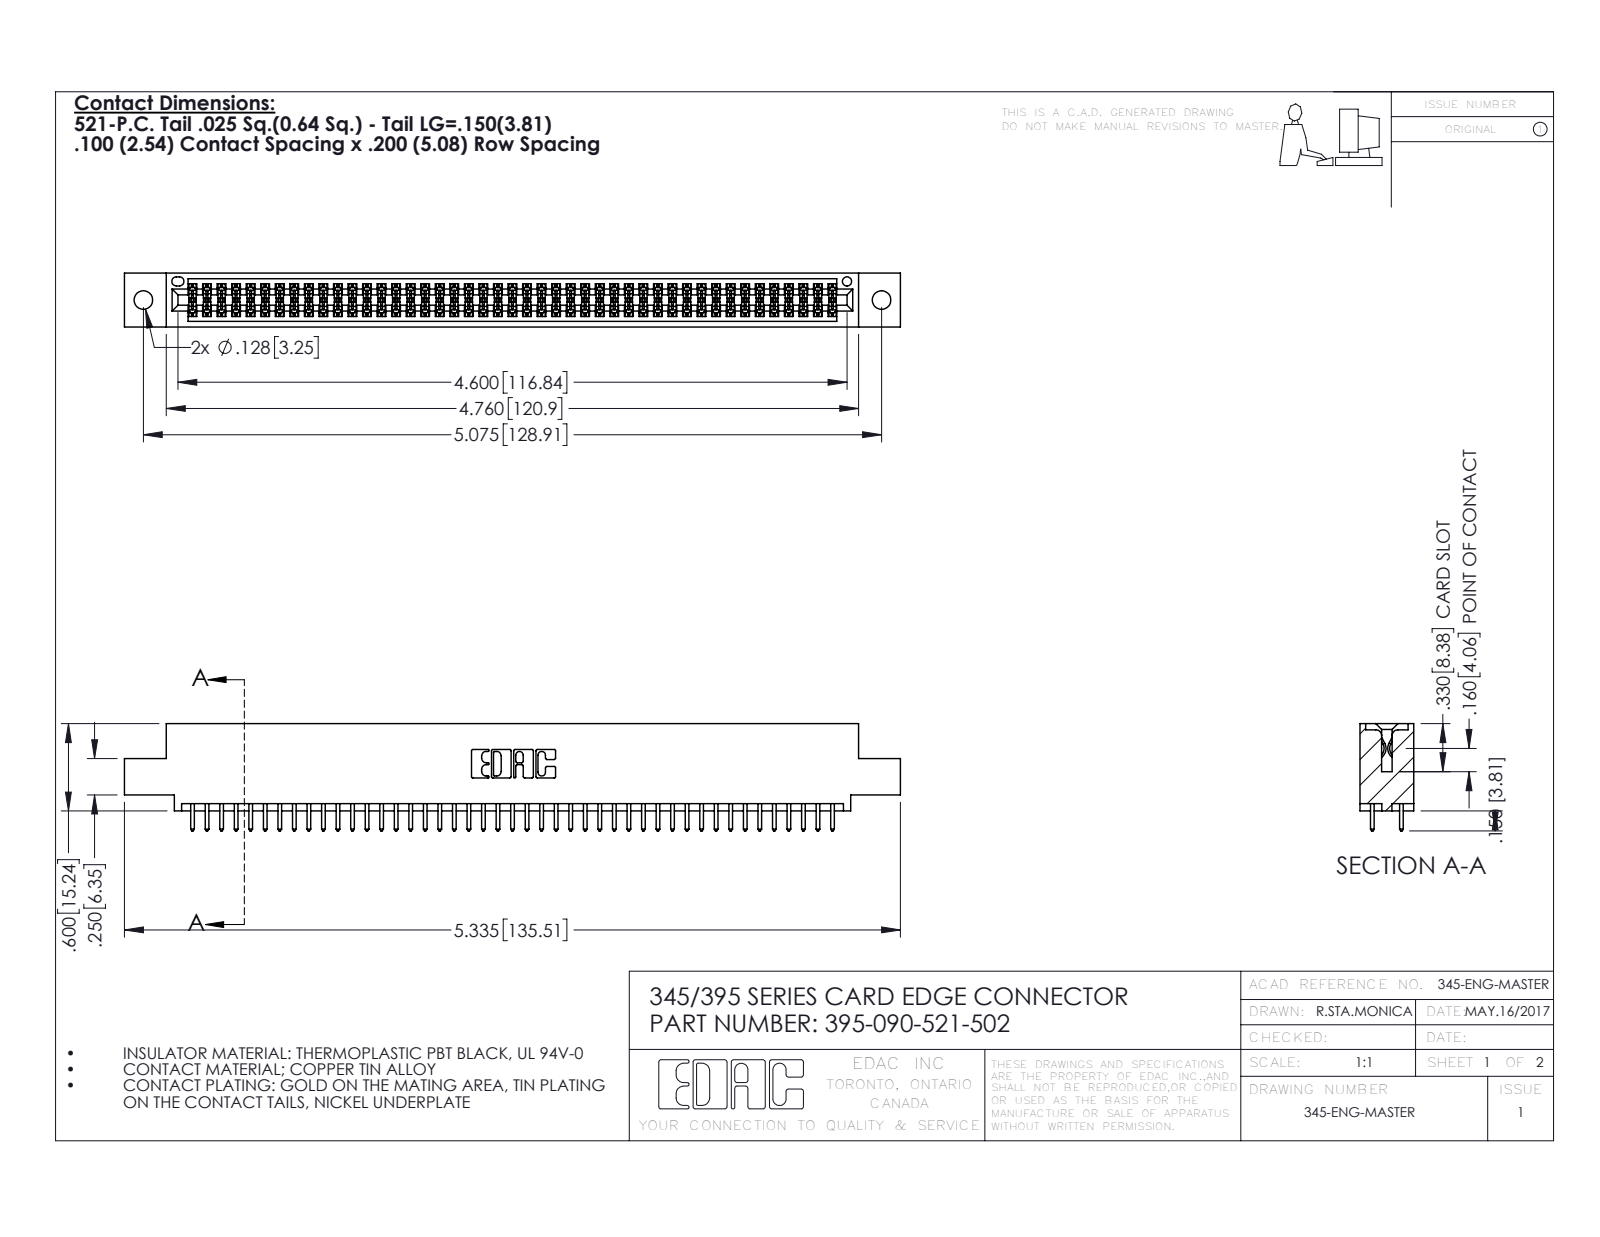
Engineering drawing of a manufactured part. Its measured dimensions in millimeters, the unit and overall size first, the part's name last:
Units: millimetres
Overall size (bounding box): 135.5 × 18.7 × 9.4
Round holes (diameter × count): ⌀3.3 ×2, ⌀1.6 ×1
Partial cylindrical surfaces — rounded edges, fillets, slot ends (radius × count): R0.2 ×135, R0.3 ×90, R0.3 ×22, R0.2 ×6, R0.8 ×6, R0.7 ×3, R0.4 ×2, R0.5 ×2
Main face-to-face distances: 7.6, 1.8, 5.1, 9.4, 2.5, 6.9, 0.6, 5.7, 4.4, 3.8
Hole centre spacings: 6.9, 122.9, 128.9
Volume: 13 000 mm³ · Surface area: 18 920 mm²
Bodies: 91 solids, 4630 faces (3054 planar, 1576 cylindrical, 0 other)
Part name (STEP PRODUCT): 345-292-001_345-293-121; 345 Part_0.110 Offset - 0.128 Dia; 395-090-521-502
STEP written by: SolidWorks 2016 (CONFIG_CONTROL_DESIGN)
